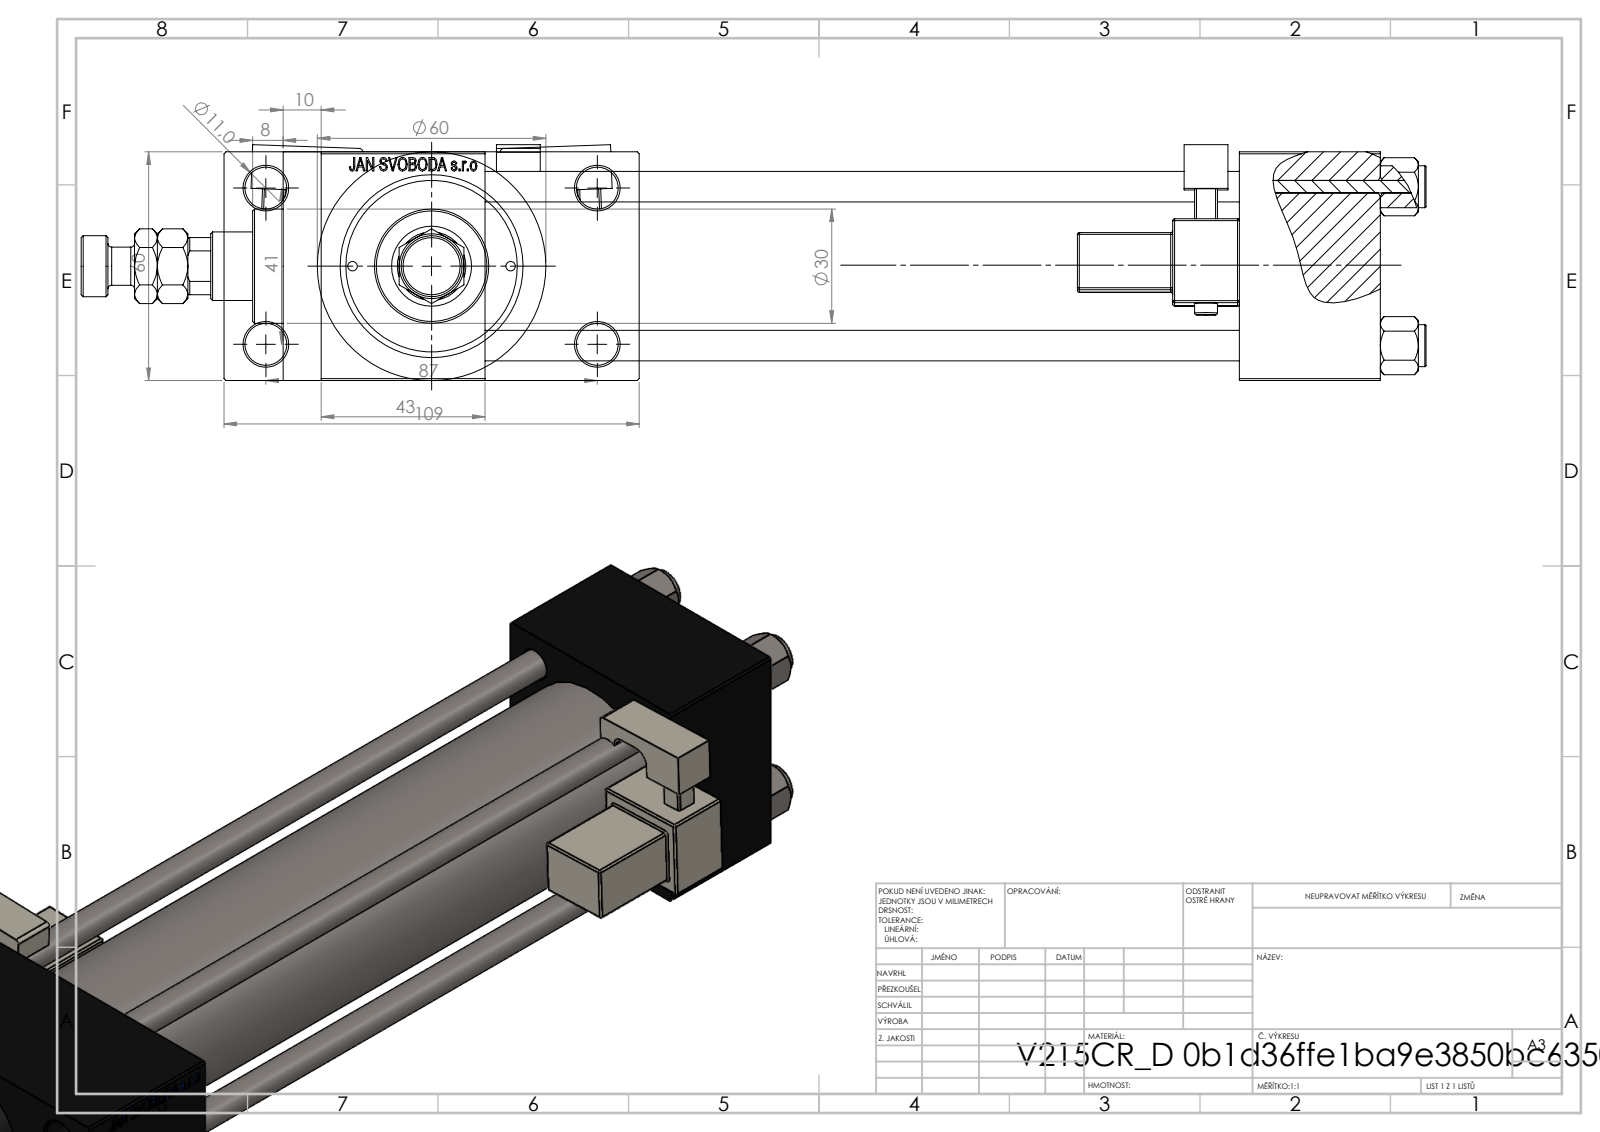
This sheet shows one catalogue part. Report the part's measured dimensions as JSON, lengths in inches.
{"part_name": "V215CR_D_TYCINKA; V215_VC_A; V215CR_VCP_D; V215CR_D_Body (+3 more)", "step_written_by": "SolidWorks 2019 (CONFIG_CONTROL_DESIGN)", "units": "inches", "bodies": {"solids": 14, "faces": 1318, "planar": 574, "cylindrical": 156, "other": 588}, "overall_size": [13.898, 4.291, 2.437], "volume_in3": 41.44, "surface_area_in2": 304.5, "round_holes": [[0.315, 4], [0.433, 4], [0.098, 2], [0.276, 2], [0.656, 2], [0.945, 2], [0.335, 1], [0.709, 1], [0.827, 1], [1.22, 1], [1.575, 1], [1.772, 1]], "round_bosses_or_shafts": [[0.433, 4], [0.236, 2], [2.362, 1], [1.811, 1], [1.181, 1], [0.63, 1], [0.394, 1]], "partial_cylinders_radius": [[0.02, 48], [0.039, 2], [0.098, 2], [0.157, 2], [0.335, 1]], "face_to_face_distances": [2.362, 7.795, 0.965, 3.327, 1.457, 9.252, 10.945, 9.488, 1.693, 4.291], "hole_center_spacings": [0.821, 0.892, 1.161, 1.206, 1.642, 1.832, 1.856, 1.893]}
